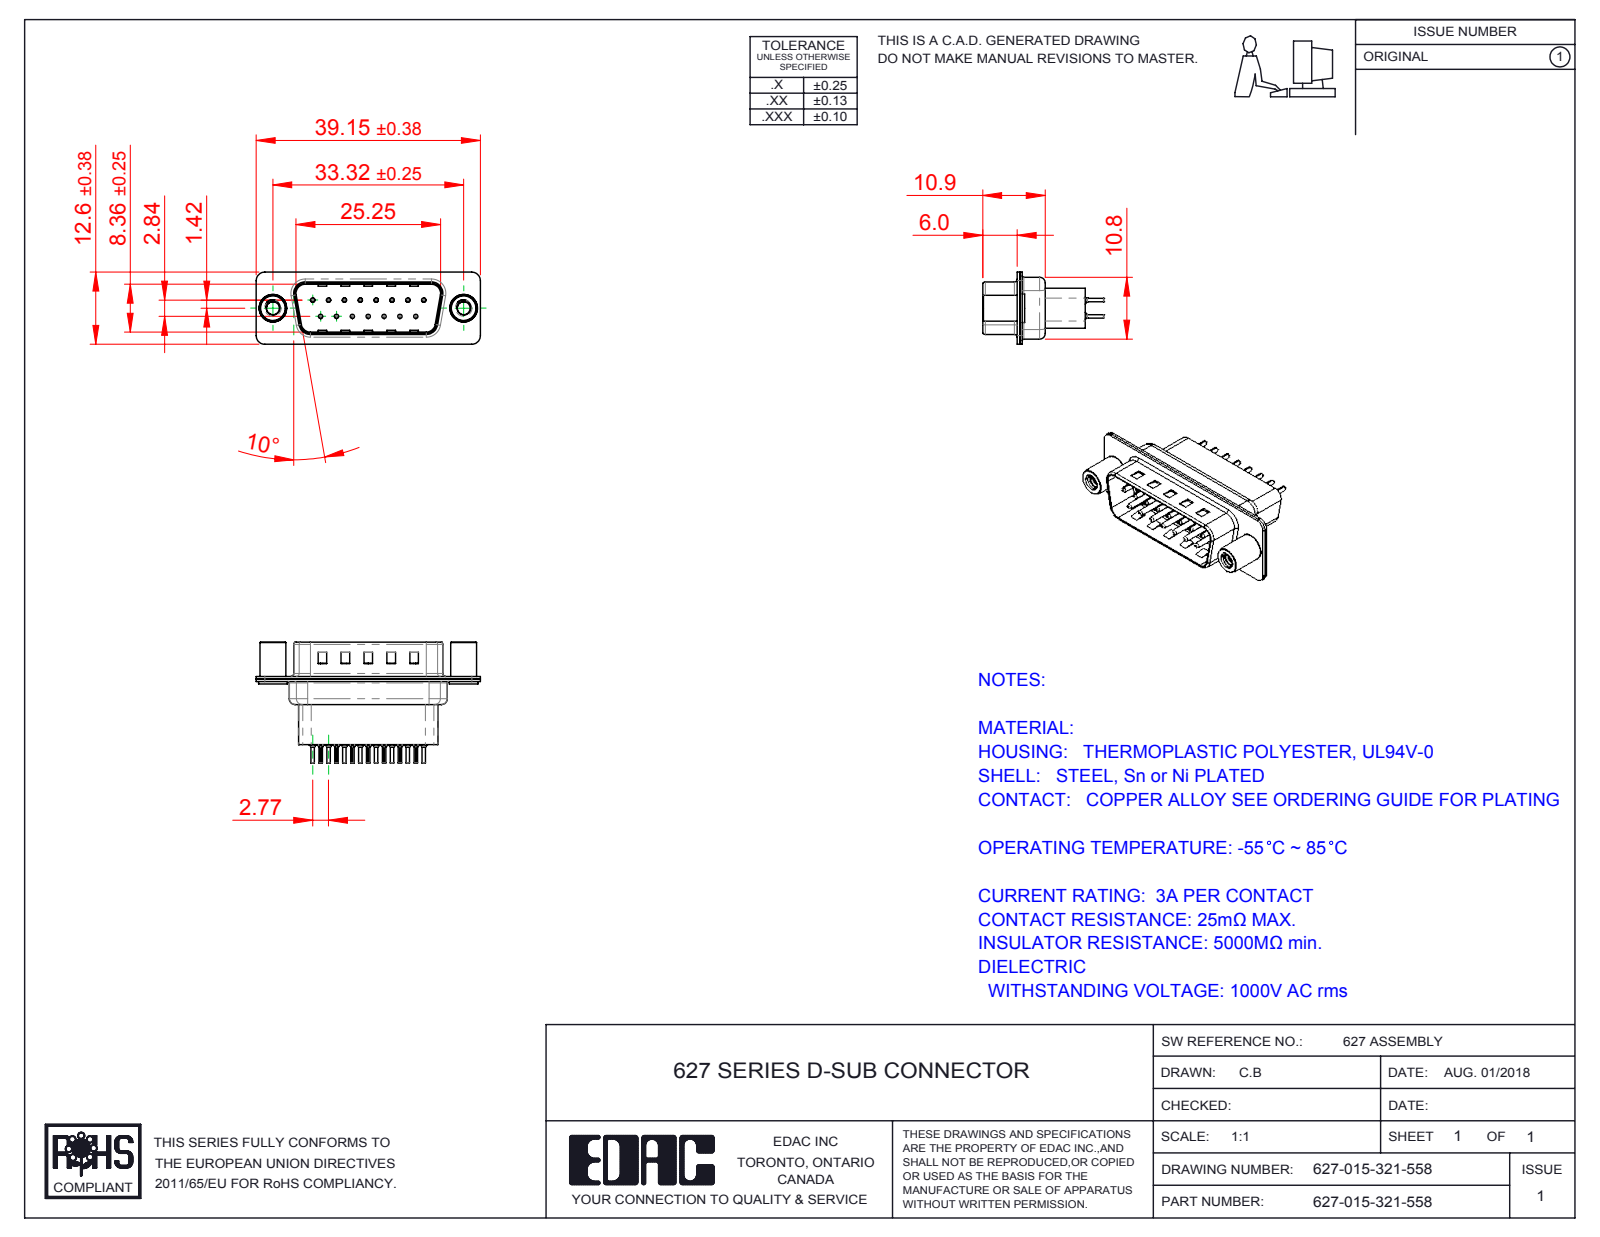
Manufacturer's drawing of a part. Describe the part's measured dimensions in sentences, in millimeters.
The part is named "627-015-321-558; 627 Housing_15 HP; 627 Shell Front_15 Contacts; 627 4-40 Threaded Standoff (+3 more)". Its 3-D file was written by "SolidWorks 2016 (CONFIG_CONTROL_DESIGN)". It is 20 solids with 1844 faces: 501 planar, 716 cylindrical and 627 other. Overall it measures 39.15 by 21.1 by 12.6 millimeters. Its volume is 2 675 cubic millimeters and its surface area 6 933 square millimeters. Round holes: 15 of diameter 0.2, 15 of diameter 0.35, 15 of diameter 1.1, 15 of diameter 1.6, 2 of diameter 2.26, 2 of diameter 4, 2 of diameter 4.8. Round bosses or shafts: 15 of diameter 2, 15 of diameter 1.5, 15 of diameter 0.75, 15 of diameter 0.6, 2 of diameter 5, 2 of diameter 4.9, 2 of diameter 4.5. Partial cylindrical surfaces (rounded edges, fillets, slot ends): 30 of radius 0.1, 16 of radius 1.5, 12 of radius 2, 8 of radius 0.5, 8 of radius 1.6, 4 of radius 0.25, 4 of radius 0.6, 4 of radius 0.65. The main face-to-face distances are 0.4, 0.45, 0.9, 0.82, 9.58, 1.5, 0.68, 7.68, 1.4, 1.08. The hole center spacings are 3.16, 2.77, 5.54, 8.31, 11.08, 5.03, 5.04, 7.48.
